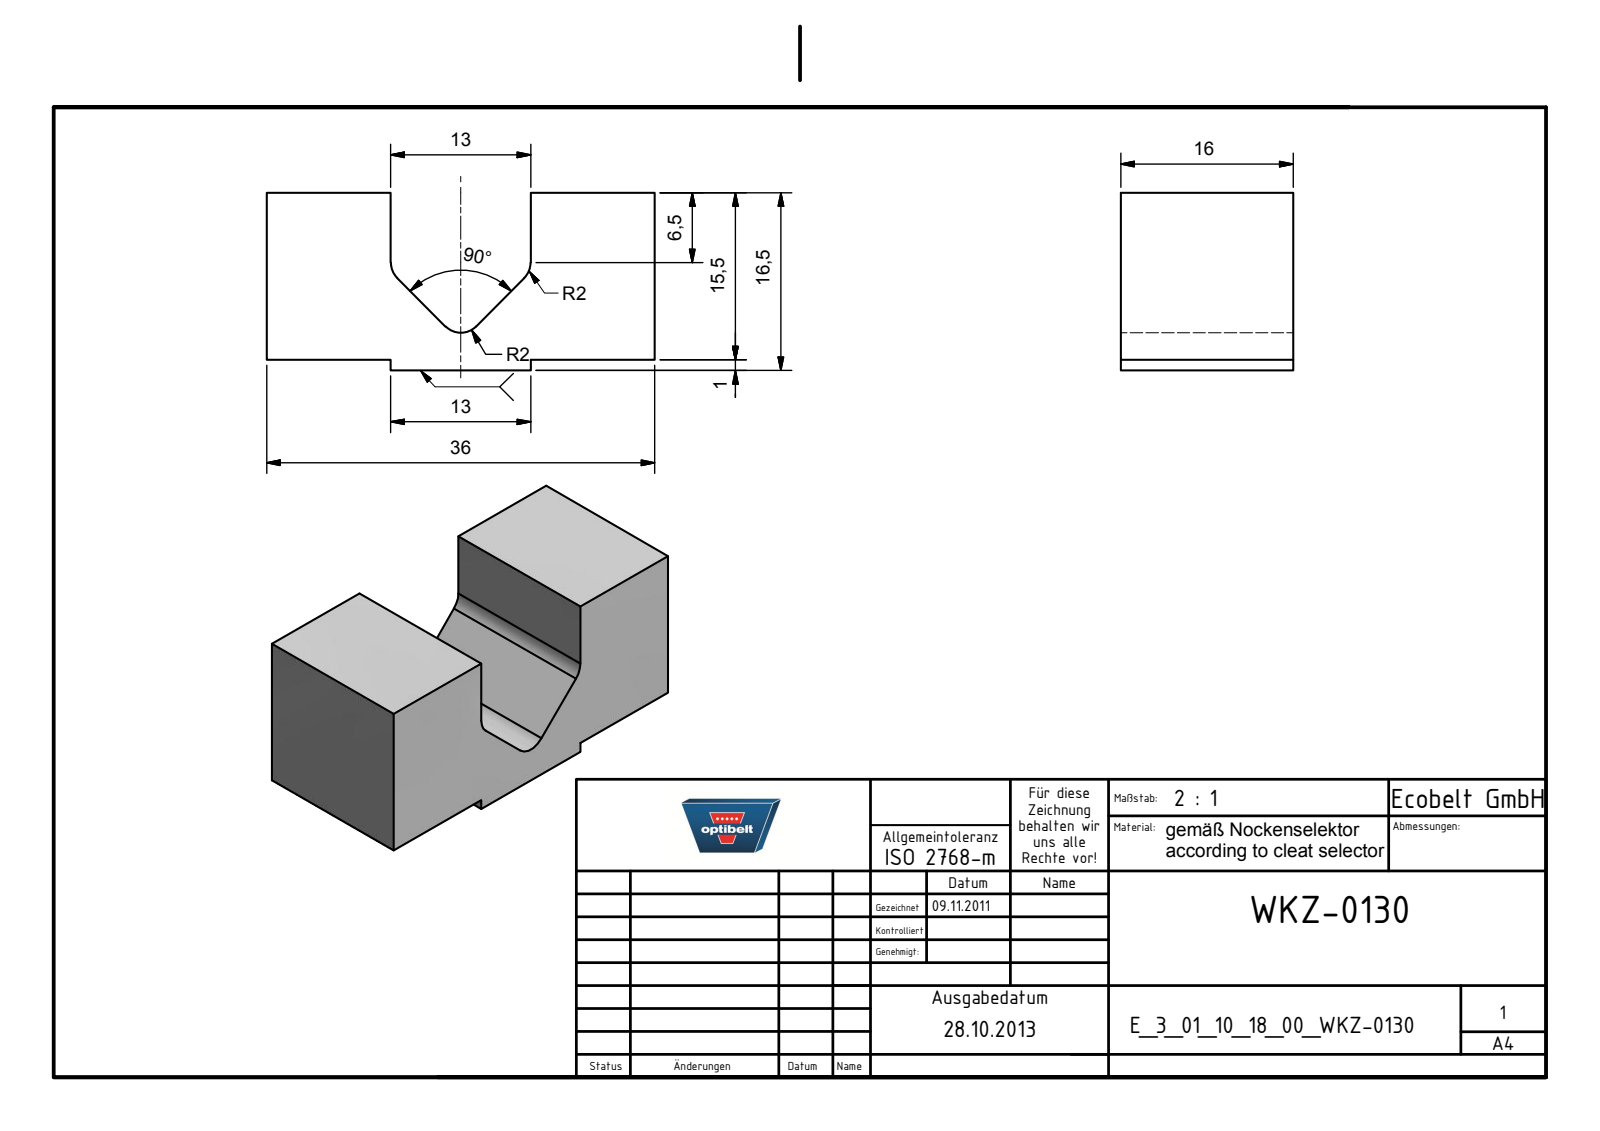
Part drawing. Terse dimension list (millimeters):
name: E_3_01_10_18_00_WKZ-0130
written by: Autodesk Inventor 2025 (AUTOMOTIVE_DESIGN)
unit: mm
bodies: 1 solid, 18 faces (15 planar, 3 cylindrical, 0 other)
size: 36 × 16.5 × 16
volume: 6 952 mm³; area: 2 853 mm²
rounds: 3× R2
face distances: 16, 15.5, 36, 11.5, 24.5, 1, 16.5, 13
